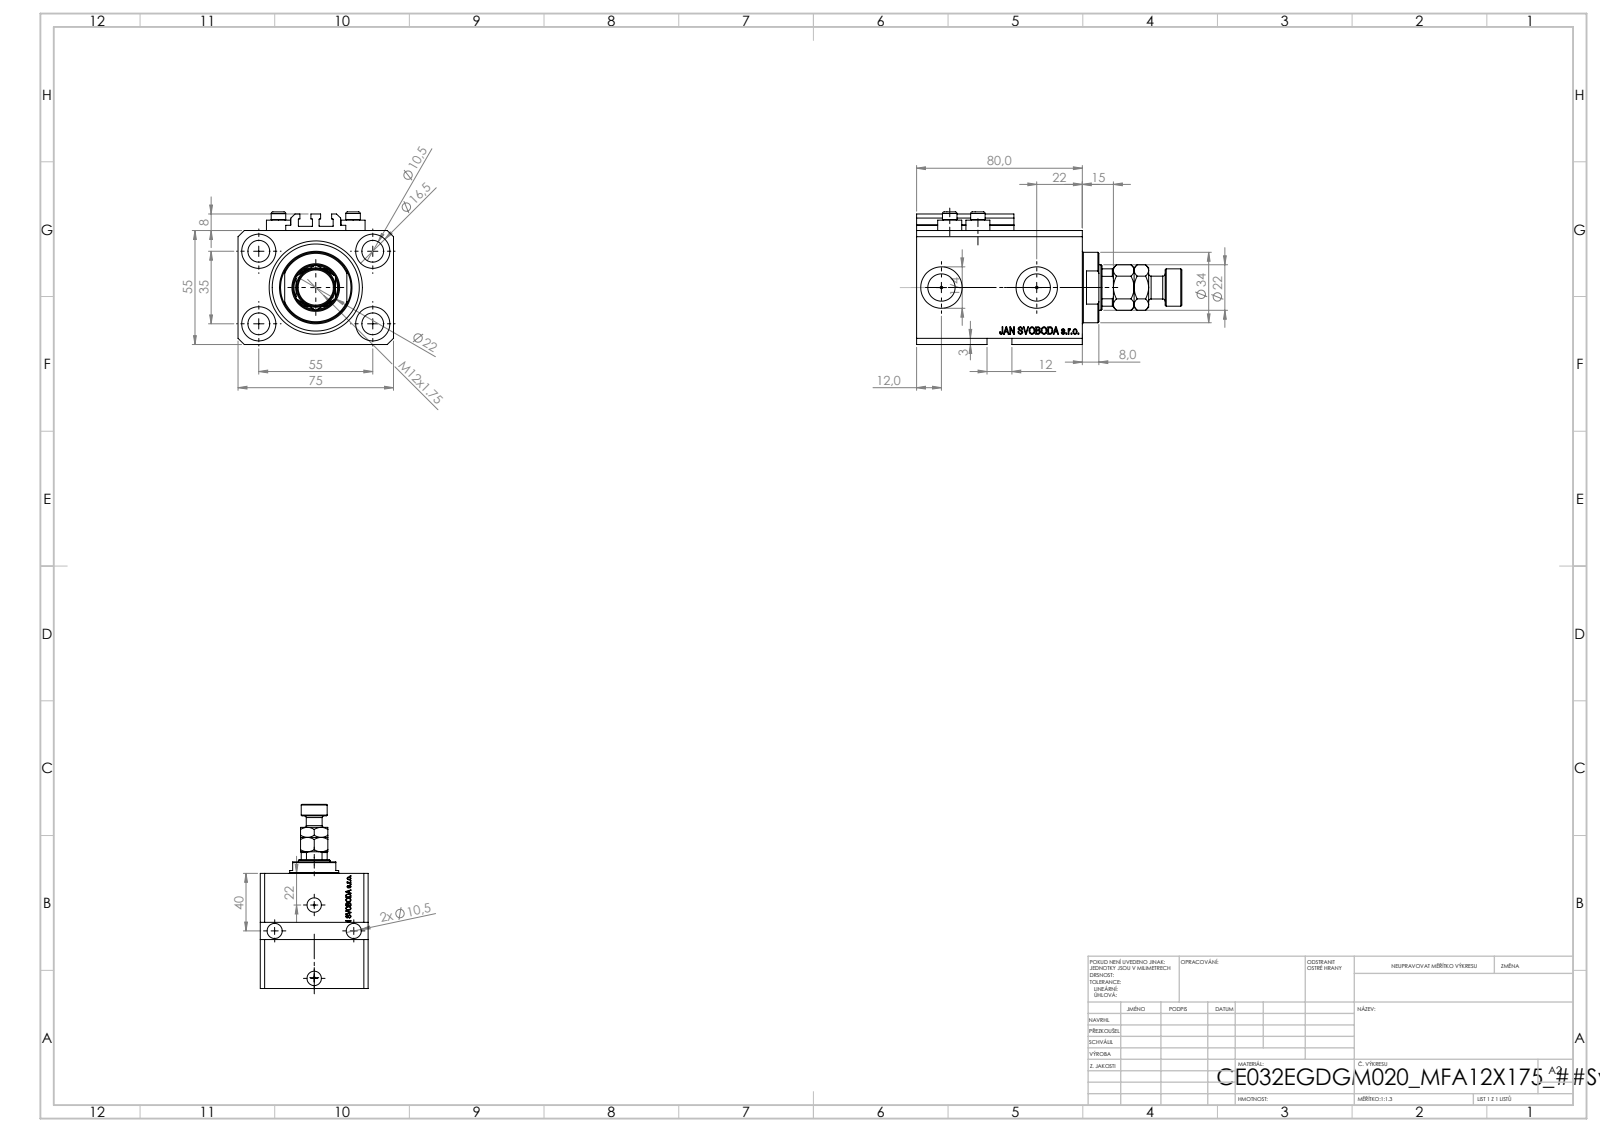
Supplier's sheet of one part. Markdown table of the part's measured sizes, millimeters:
| quantity | value |
| --- | --- |
| part name | ALLEN BOLT V250CE; MFA; V250CE_VC_E; V250CE_C_VCP (+1 more) |
| STEP written by | SolidWorks 2019 (CONFIG_CONTROL_DESIGN) |
| units | millimeters |
| bodies | 9 solids, 1132 faces (534 planar, 142 cylindrical, 456 other) |
| overall size | 128 × 75 × 64 |
| volume | 288 342 mm³ |
| surface area | 78 309 mm² |
| round holes (diameter × count) | 10.5 × 7, 1.25 × 4, 4 × 4, 16.5 × 4, 10 × 2, 13.16 × 2, 20 × 2, 22 × 1, 32 × 1, 45 × 1 |
| round bosses / shafts (diameter × count) | 11.6 × 4, 7 × 4, 34 × 1, 18 × 1, 11 × 1 |
| partial cylindrical surfaces (radius × count) | 0.2 × 10, 10.5 × 1 |
| main face-to-face distances | 55, 75, 15, 65, 80, 9.9, 55.1, 3, 70.1, 54 |
| hole center spacings | 32.6, 55, 13.6, 14.09, 19.89, 20.12, 25.81, 28.48 |
